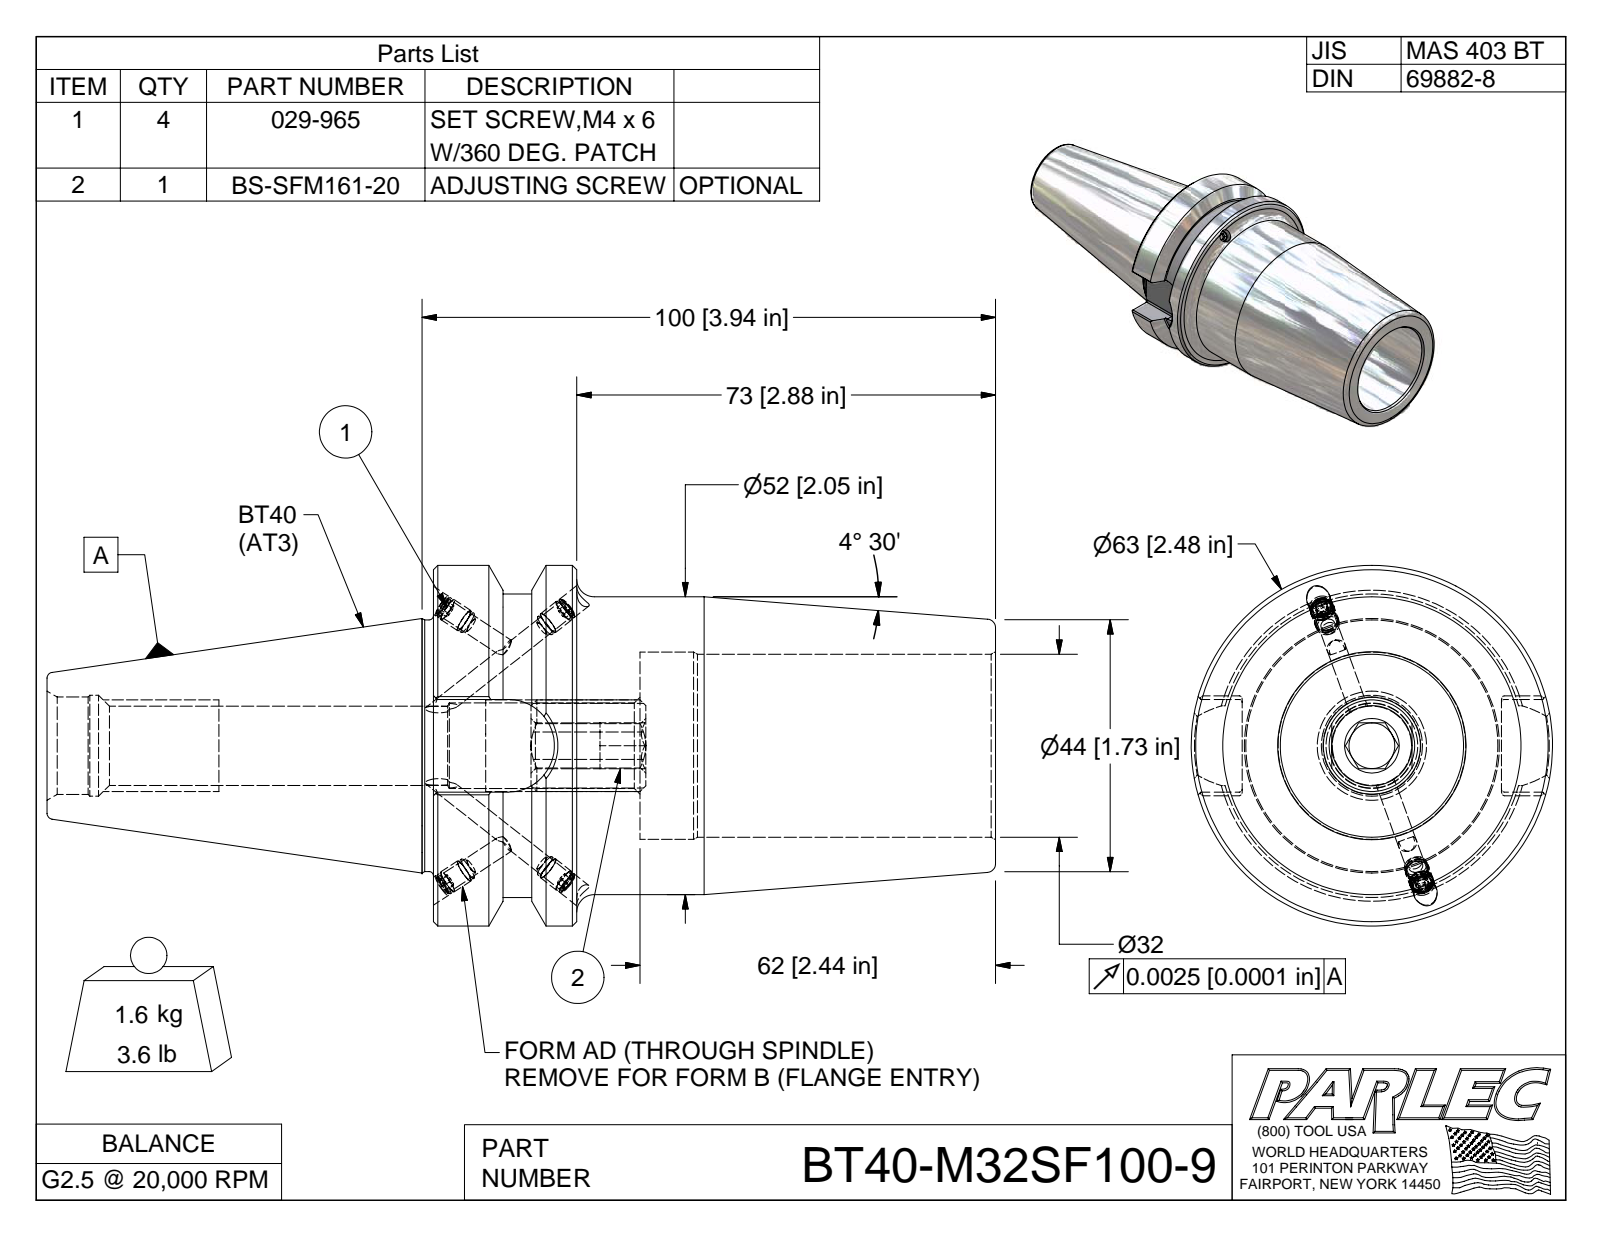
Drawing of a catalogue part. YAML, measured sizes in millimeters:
part_name: "BT40-M32SF100-9; BT40BC-M32SF100-9-1; 029-965; BS-SFM161-20"
step_written_by: "Autodesk Inventor 2009 (AUTOMOTIVE_DESIGN)"
units: millimeters
bodies: {solids: 6, faces: 174, planar: 79, cylindrical: 43, other: 52}
overall_size: [165.4, 63, 63]
volume: 208400
surface_area: 42610
round_holes:
  - {diameter: 3.3, count: 4}
  - {diameter: 4.1, count: 4}
  - {diameter: 17.6, count: 1}
  - {diameter: 32, count: 1}
  - {diameter: 32.7, count: 1}
round_bosses_or_shafts:
  - {diameter: 4.2, count: 4}
  - {diameter: 4, count: 4}
  - {diameter: 63, count: 1}
  - {diameter: 53, count: 1}
  - {diameter: 52, count: 1}
  - {diameter: 44.5, count: 1}
  - {diameter: 43.9, count: 1}
partial_cylinders:
  - {radius: 0.5, count: 8}
  - {radius: 8, count: 1}
  - {radius: 8.1, count: 1}
face_to_face_distances: [36, 98, 62, 25, 11, 73, 15.6, 29.6, 45.2, 67.4]
